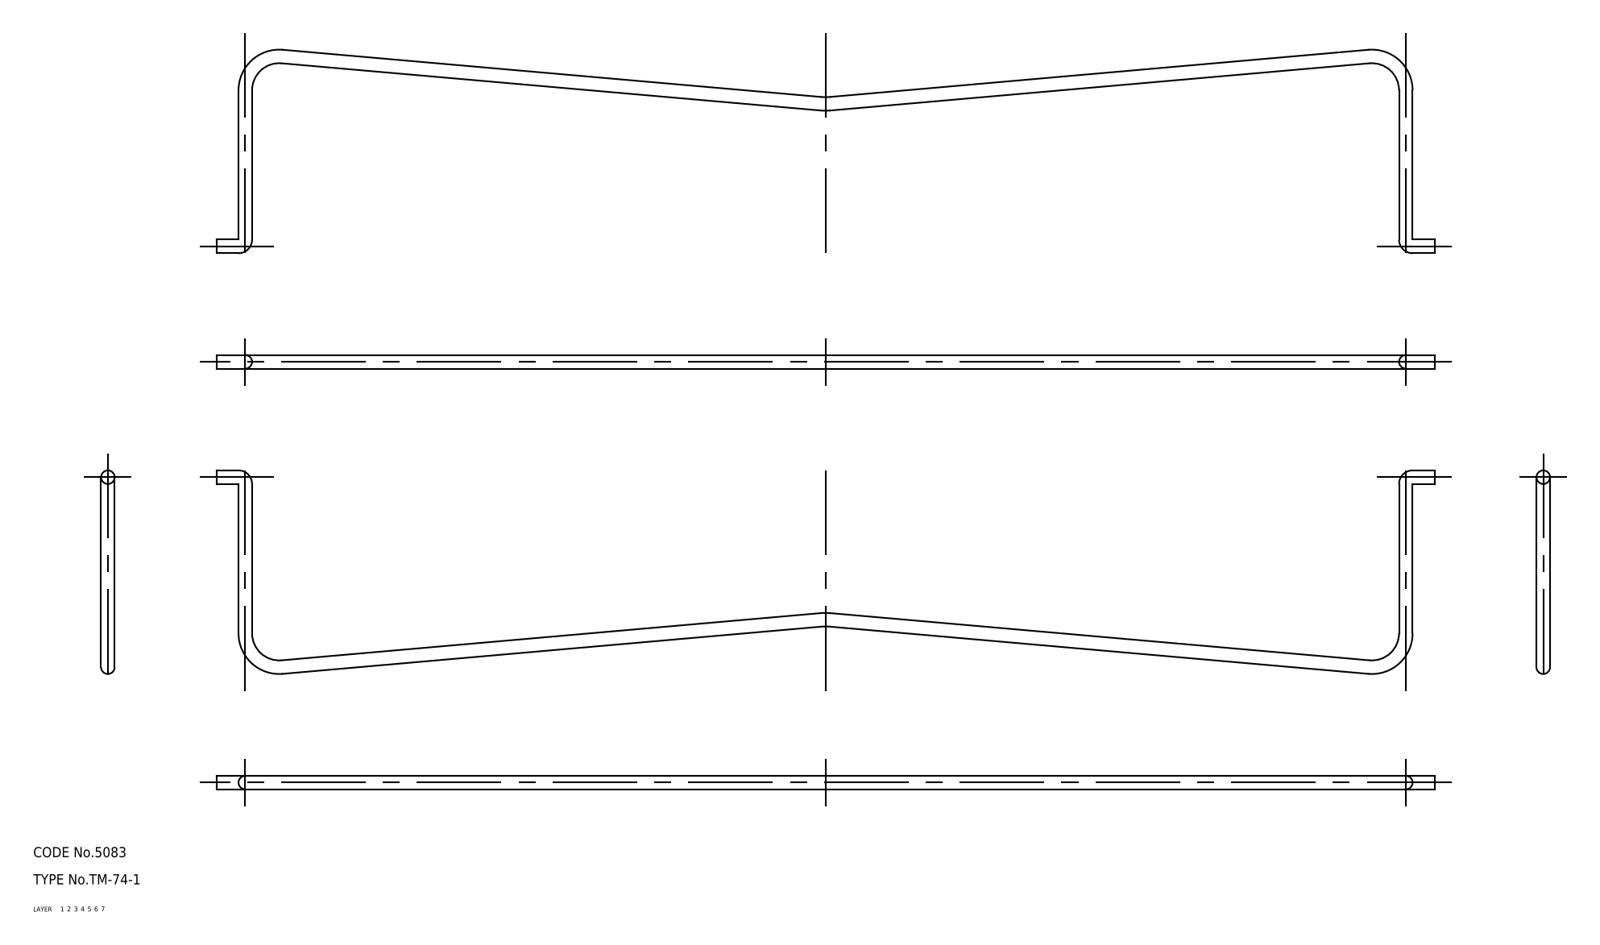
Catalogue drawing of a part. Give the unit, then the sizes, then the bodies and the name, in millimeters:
Units: millimetres
Overall size (bounding box): 359 × 60 × 4
Volume: 5 926 mm³ · Surface area: 5 829 mm²
Bodies: 1 solid, 24 faces (0 planar, 0 cylindrical, 24 other)
Part name (STEP PRODUCT): stand
STEP written by: CADfix (AUTOMOTIVE_DESIGN)
